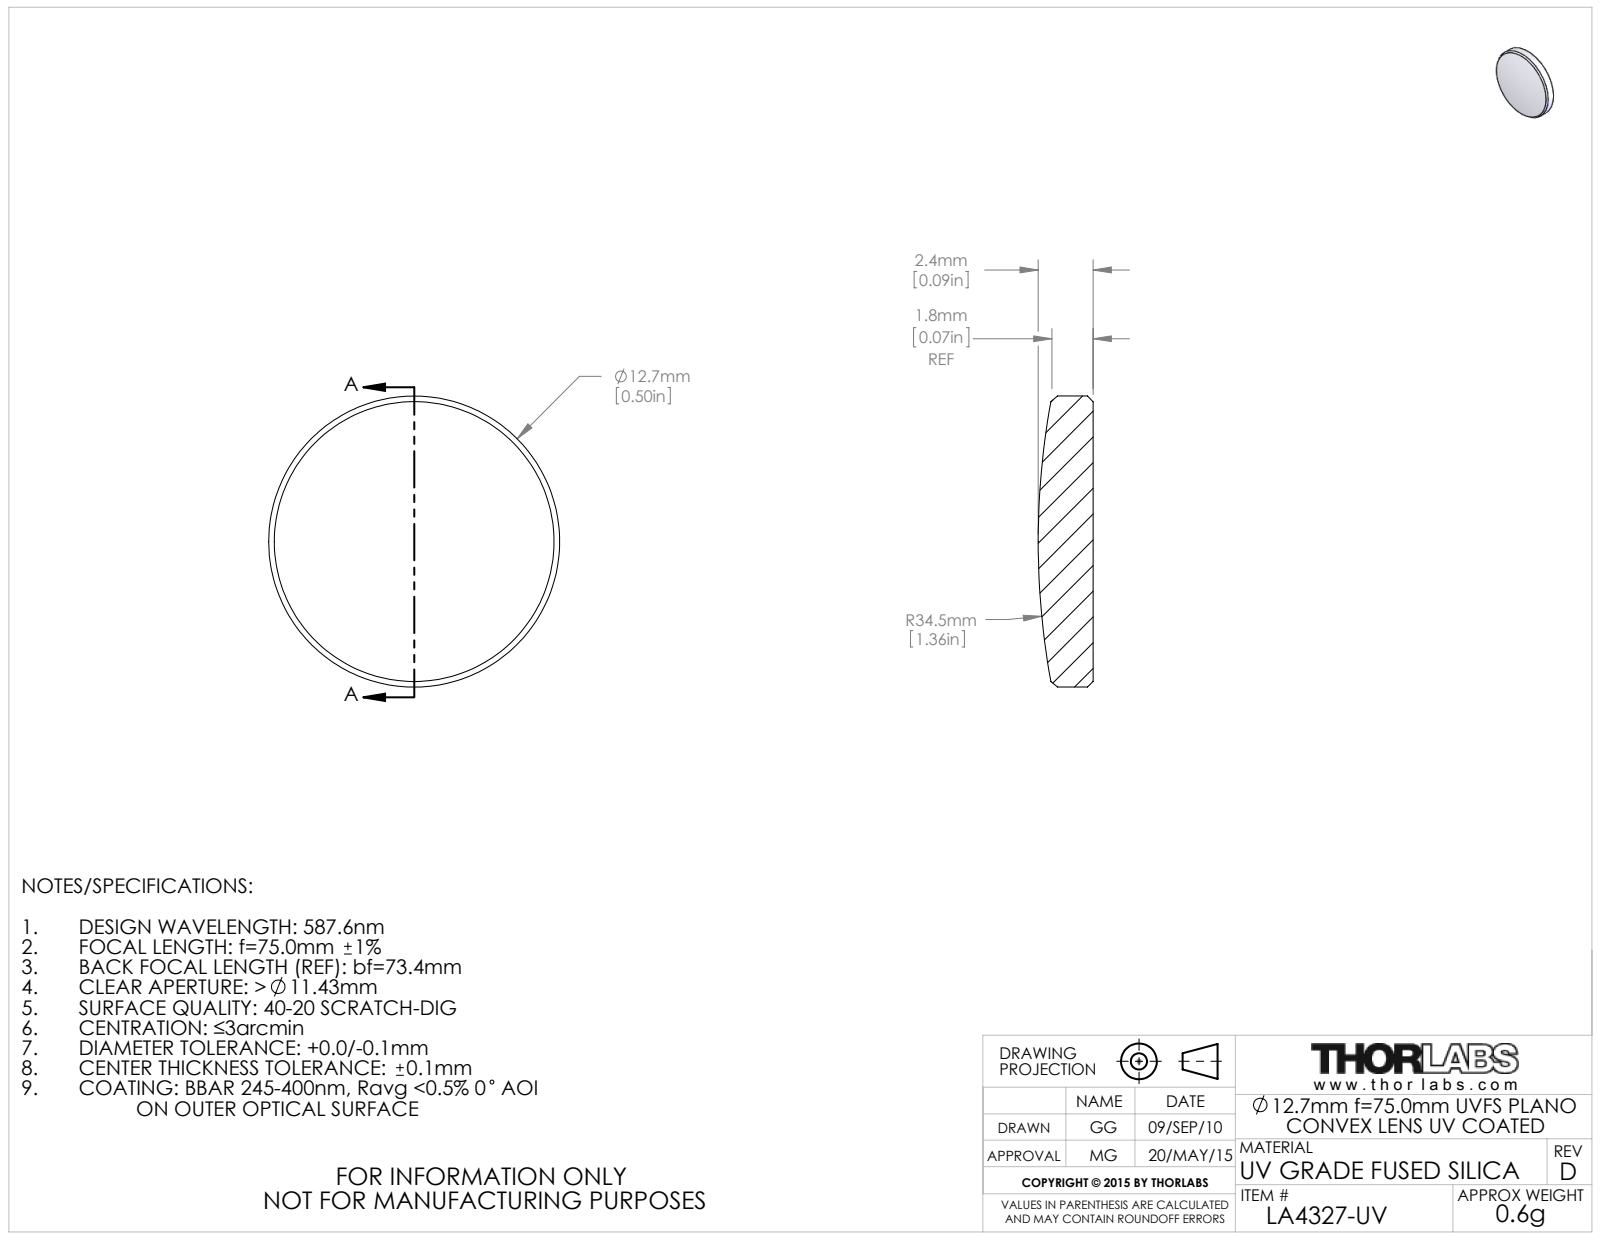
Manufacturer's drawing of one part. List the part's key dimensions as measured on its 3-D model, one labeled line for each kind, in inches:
Part name (STEP PRODUCT): 4276-E0W
STEP written by: SolidWorks 2014 (CONFIG_CONTROL_DESIGN)
Units: inches
Bodies: 1 solid, 9 faces (1 planar, 2 cylindrical, 6 other)
Overall size (bounding box): 0.5 × 0.5 × 0.094
Volume: 0.016 in³ · Surface area: 0.49 in²
Round bosses / shafts (diameter × count): ⌀0.5 ×1
